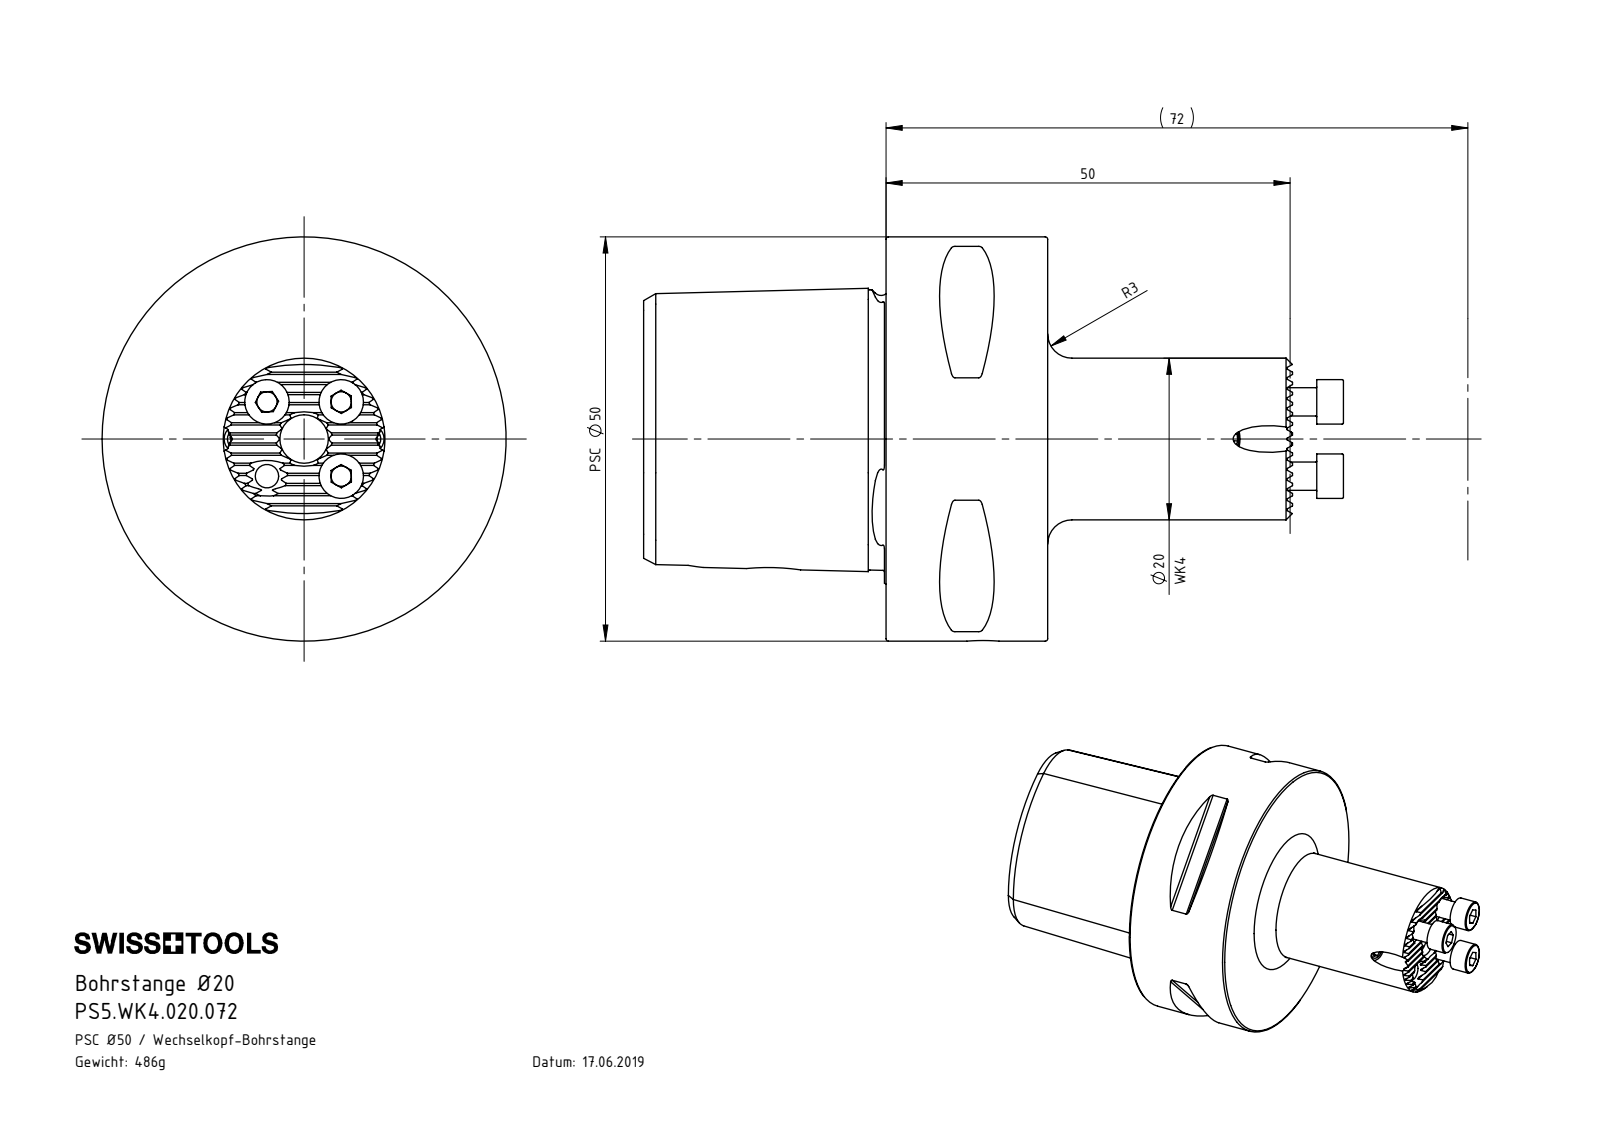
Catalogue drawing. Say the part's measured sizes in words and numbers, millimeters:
The part is named "DIN 3771 - 6x1; PS5.WK4.020.072; ISO 4026 - M3 x 3; ISCAR M3.5 x 10 (+1 more)". Its 3-D file was written by "SolidWorks 2017 (AUTOMOTIVE_DESIGN)". It is 7 solids with 341 faces: 184 planar, 73 cylindrical and 84 other. Overall it measures 86.6 by 50 by 50 millimeters. Its volume is 61 918 cubic millimeters and its surface area 17 007 square millimeters. Round holes: 5 of diameter 2.5, 4 of diameter 2.9, 2 of diameter 3.3, 1 of diameter 4, 1 of diameter 6, 1 of diameter 6.1, 1 of diameter 6.8, 1 of diameter 7.4, 1 of diameter 14.5, 1 of diameter 21, 1 of diameter 24. Round bosses or shafts: 3 of diameter 5.5, 3 of diameter 3.5, 2 of diameter 3, 1 of diameter 50, 1 of diameter 20. Partial cylindrical surfaces (rounded edges, fillets, slot ends): 15 of radius 0.12, 8 of radius 0.5, 1 of radius 4. The main face-to-face distances are 20, 30, 50, 19.18, 4.33, 1.08, 3.25, 44.4, 10, 5.41. The hole center spacings are 6.51, 9.2, 13.01, 26.
